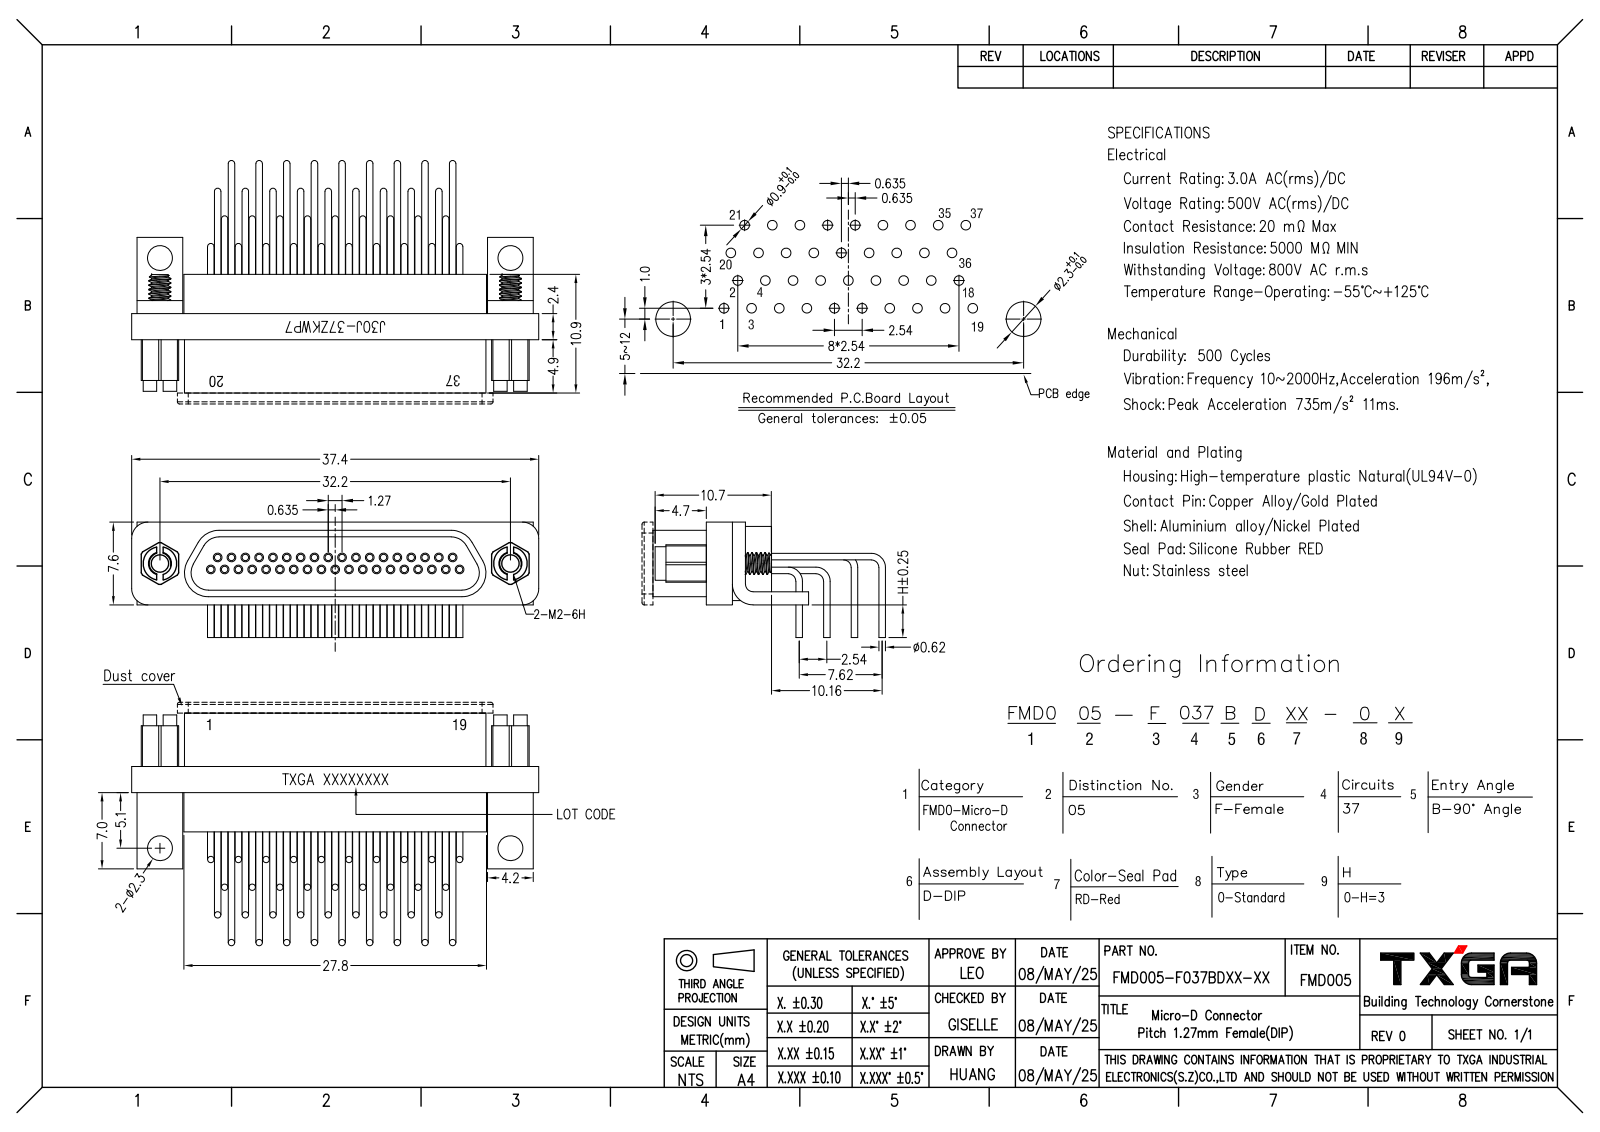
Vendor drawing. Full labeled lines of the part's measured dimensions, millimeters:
Part name (STEP PRODUCT): FMD005-F037BDRD-00
STEP written by: SolidWorks 2021 (CONFIG_CONTROL_DESIGN)
Units: millimetres
Bodies: 1 solid, 1874 faces (903 planar, 548 cylindrical, 423 other)
Overall size (bounding box): 37.4 × 21.36 × 10.6
Volume: 1 873 mm³ · Surface area: 3 651 mm²
Round holes (diameter × count): ⌀0.6 ×37, ⌀1.6 ×2, ⌀1.8 ×2, ⌀2.3 ×2, ⌀3.2 ×2
Round bosses / shafts (diameter × count): ⌀0.8 ×37, ⌀0.6 ×37, ⌀3.1 ×2, ⌀2 ×2
Partial cylindrical surfaces — rounded edges, fillets, slot ends (radius × count): R0.2 ×12, R0.3 ×12, R1.5 ×4, R1.8 ×4, R1.15 ×2, R1.4 ×2, R1.6 ×2, R2 ×2
Main face-to-face distances: 0.6, 5.5, 0.75, 1.35, 6.85, 0.95, 0.35, 5.85, 6.45, 7.2
Hole centre spacings: 1.27, 2.54, 1.42, 3.81, 2.29, 5.08, 6.35, 7.62
